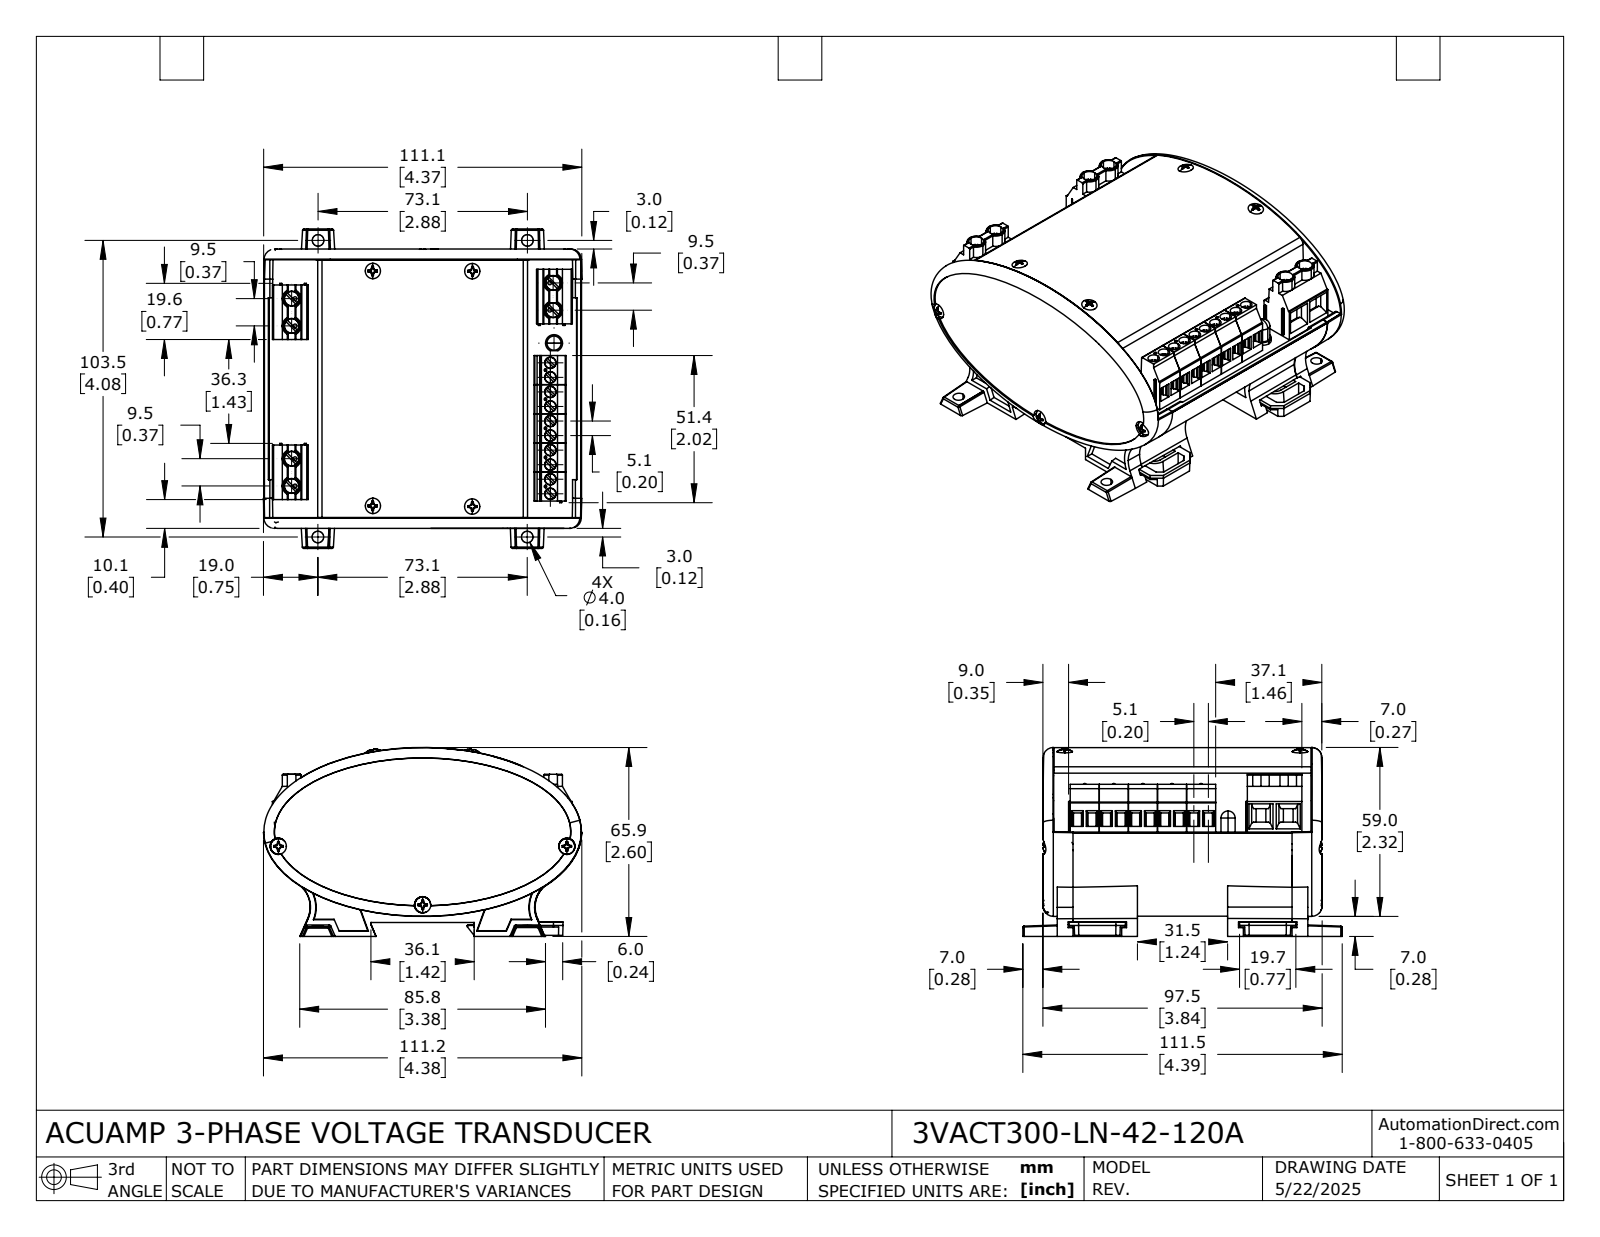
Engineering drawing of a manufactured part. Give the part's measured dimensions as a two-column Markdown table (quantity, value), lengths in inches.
| quantity | value |
| --- | --- |
| part name | 3VACT300-LN-42-120A |
| STEP written by | SolidWorks 2024 (AUTOMOTIVE_DESIGN) |
| units | inches |
| bodies | 26 solids, 2967 faces (1482 planar, 844 cylindrical, 641 other) |
| overall size | 7.429 × 4.374 × 2.597 |
| volume | 11.76 in³ |
| surface area | 284.7 in² |
| round holes (diameter × count) | 0.05 × 12, 0.157 × 10, 0.08 × 6, 0.205 × 6, 0.126 × 4, 0.111 × 3, 0.28 × 3 |
| round bosses / shafts (diameter × count) | 0.051 × 16, 0.15 × 10, 0.112 × 10, 0.067 × 10, 0.197 × 6, 0.018 × 4, 0.234 × 1, 0.194 × 1 |
| partial cylindrical surfaces (radius × count) | 0.006 × 38, 0.039 × 20, 0.02 × 17, 0.008 × 12, 0.012 × 8, 0.01 × 6, 0.128 × 6, 0.018 × 4 |
| main face-to-face distances | 0.063, 0.128, 6.709, 0.084, 6.838, 6.581, 0.394, 6.444, 0.266, 6.315 |
| hole center spacings | 0.2, 0.4, 0.6, 0.8, 1, 1.2, 0.2, 0.2 |
